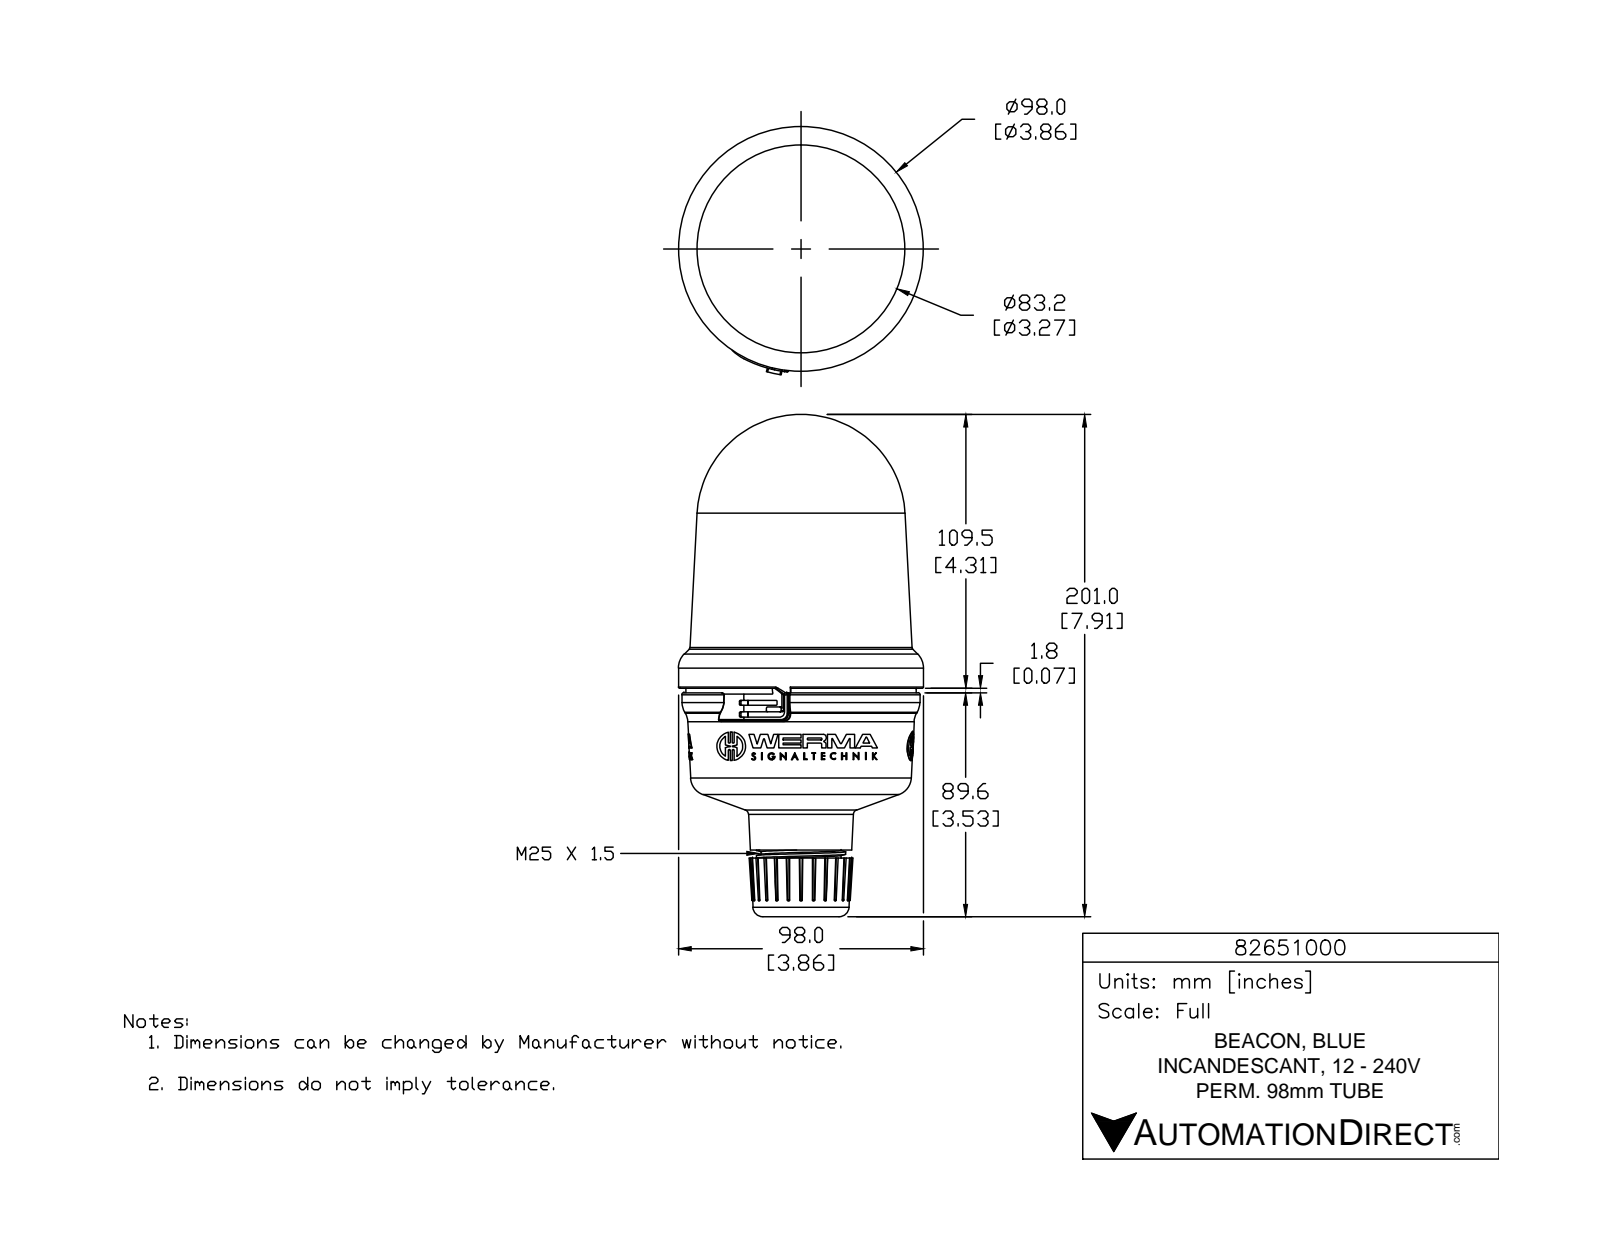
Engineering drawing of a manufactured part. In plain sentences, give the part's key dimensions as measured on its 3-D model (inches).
The part is named "82651000". Its 3-D file was written by "SolidWorks 2015 (AUTOMOTIVE_DESIGN)". It is 1 solid with 1006 faces: 554 planar, 189 cylindrical and 263 other. Overall it measures 7.914 by 3.912 by 3.858 inches. Its volume is 54.7 cubic inches and its surface area 91.39 square inches. Round holes: 3 of diameter 0.078, 1 of diameter 1.013, 1 of diameter 1.024. Round bosses or shafts: 3 of diameter 0.452, 3 of diameter 0.113, 1 of diameter 3.858, 1 of diameter 1.409, 1 of diameter 1.261. Partial cylindrical surfaces (rounded edges, fillets, slot ends): 12 of radius 0.02, 9 of radius 0.007, 6 of radius 0.007, 6 of radius 0.016, 6 of radius 0.016, 6 of radius 0.016, 6 of radius 0.262, 3 of radius 0.006. The main face-to-face distances are 2.214, 0.462, 2.676, 0.335, 0.127, 2.548, 2.603, 2.476, 2.141, 0.073.
